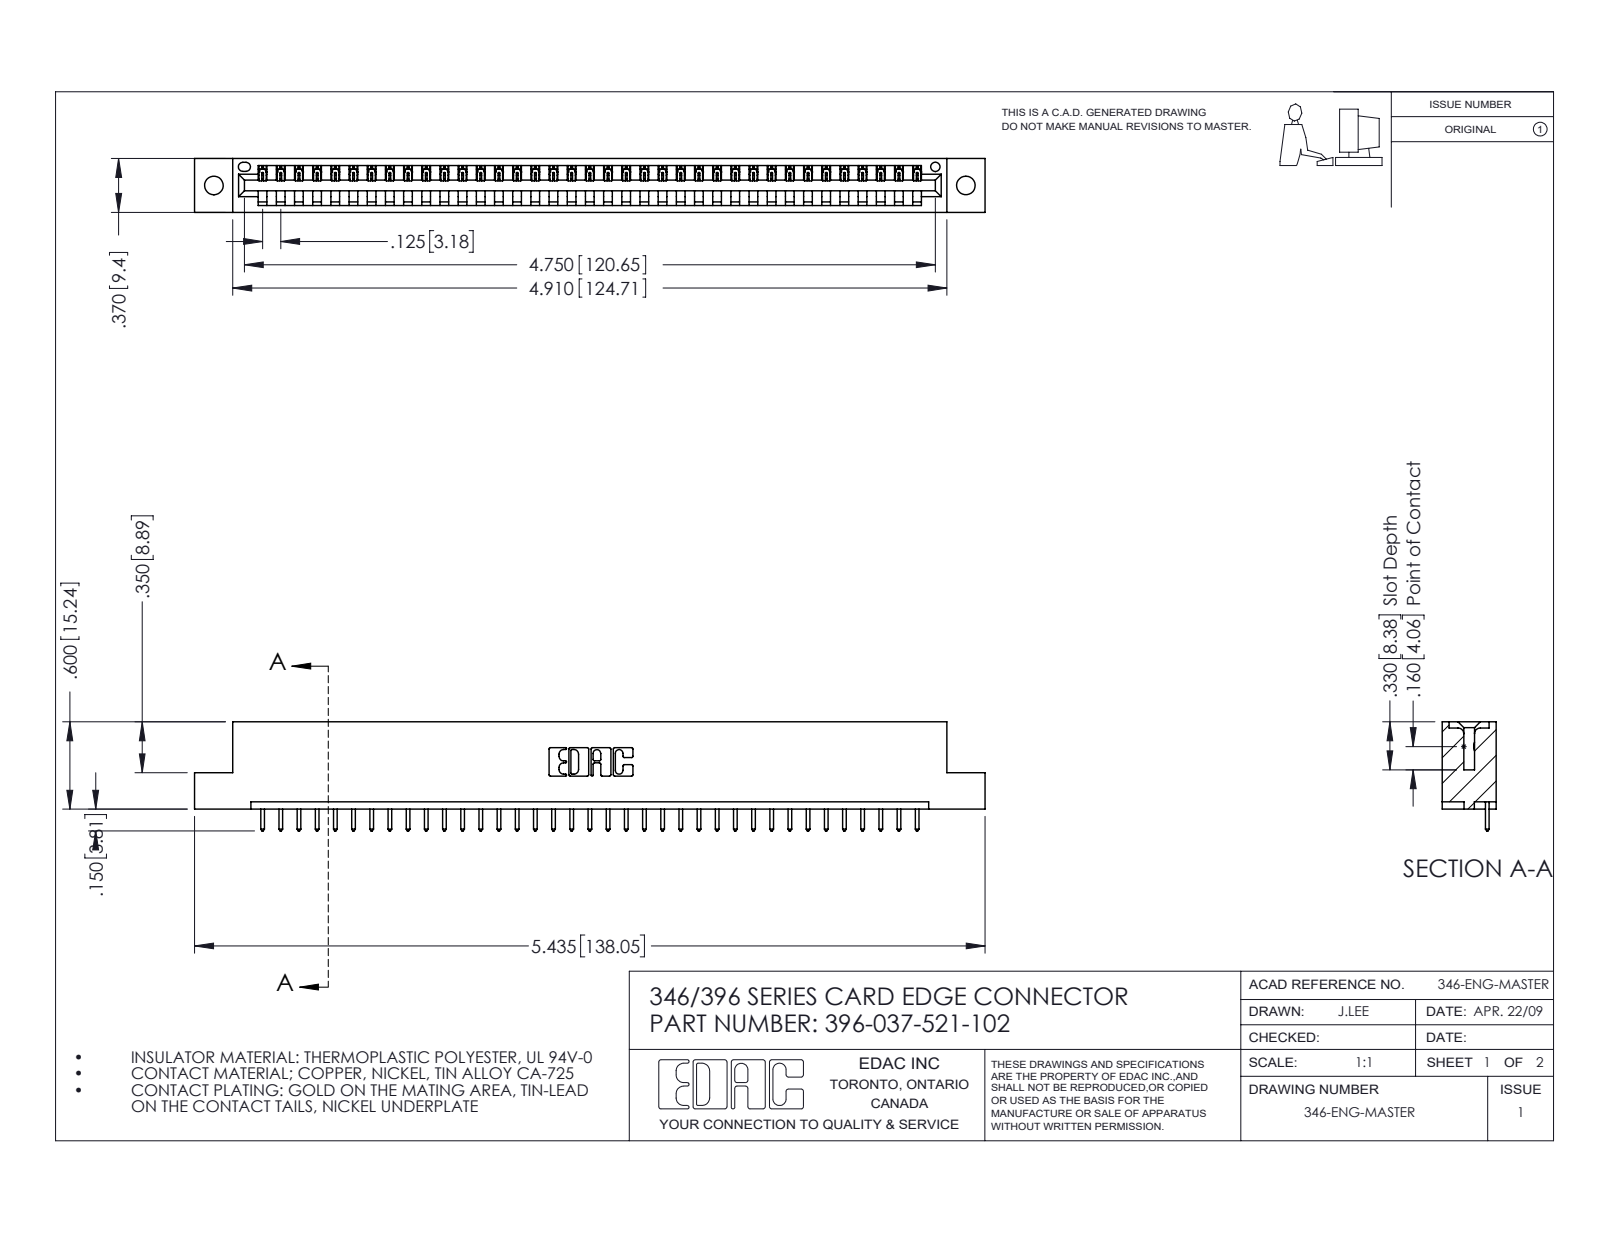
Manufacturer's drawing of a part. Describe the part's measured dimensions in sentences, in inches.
The part is named "345-292-001_345-293-121; 346 Part_Flush Mounting Lugs - 0.128 Dia; 396-037-521-102". Its 3-D file was written by "SolidWorks 2016 (CONFIG_CONTROL_DESIGN)". It is 38 solids with 2268 faces: 1556 planar, 712 cylindrical and 0 other. Overall it measures 5.435 by 0.75 by 0.37 inches. Its volume is 0.796 cubic inches and its surface area 24.11 square inches. Round holes: 2 of diameter 0.128, 1 of diameter 0.064. Partial cylindrical surfaces (rounded edges, fillets, slot ends): 74 of radius 0.006, 74 of radius 0.01, 22 of radius 0.01, 6 of radius 0.007, 6 of radius 0.031, 3 of radius 0.026, 2 of radius 0.031, 2 of radius 0.04. The main face-to-face distances are 0.048, 0.322, 0.37, 0.25, 0.072, 0.298, 0.025, 0.148, 0.222, 0.1. The hole center spacings are 0.246, 4.961, 5.17.
